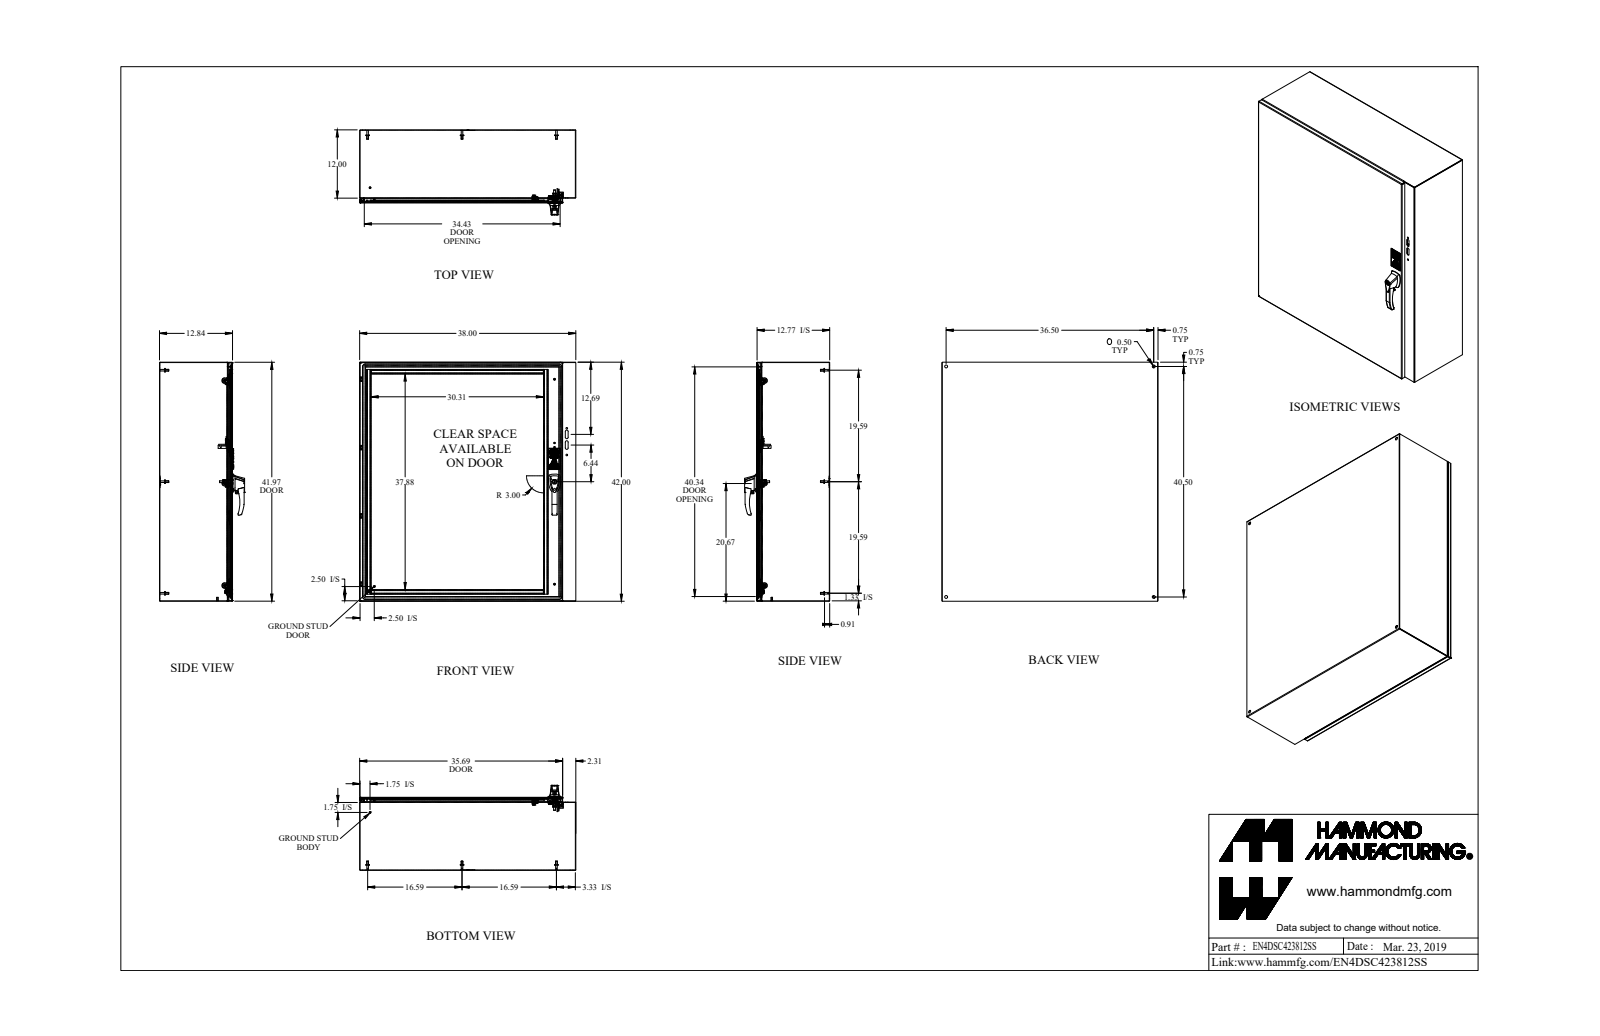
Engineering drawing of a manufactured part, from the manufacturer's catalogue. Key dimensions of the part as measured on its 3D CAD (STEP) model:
Part name (STEP PRODUCT): EN4DSC423812SS
STEP written by: SolidWorks 2019 (AUTOMOTIVE_DESIGN)
Units: inches
Bodies: 75 solids, 1578 faces (889 planar, 476 cylindrical, 213 other)
Overall size (bounding box): 42 × 38 × 14.952
Volume: 433.8 in³ · Surface area: 11 921 in²
Round holes (diameter × count): ⌀0.176 ×6, ⌀0.5 ×4, ⌀0.196 ×3, ⌀0.25 ×3, ⌀0.265 ×3, ⌀0.413 ×3, ⌀0.156 ×2, ⌀0.173 ×2, ⌀0.215 ×2, ⌀0.256 ×2, ⌀0.281 ×2, ⌀0.313 ×2
Round bosses / shafts (diameter × count): ⌀0.625 ×9, ⌀0.25 ×9, ⌀0.313 ×8, ⌀0.27 ×8, ⌀0.156 ×6, ⌀0.375 ×5, ⌀1 ×3, ⌀0.63 ×2
Partial cylindrical surfaces — rounded edges, fillets, slot ends (radius × count): R0.043 ×24, R0.081 ×24, R0.036 ×18, R0.108 ×18, R0.25 ×15, R0.03 ×14, R0.062 ×14, R0.125 ×14
Main face-to-face distances: 0.072, 12.765, 12.693, 12.837, 37.928, 41.928, 37.856, 38, 41.856, 42
Hole centre spacings: 18, 1.11, 2.883, 18, 18.001, 32.722, 36.001, 36.5
